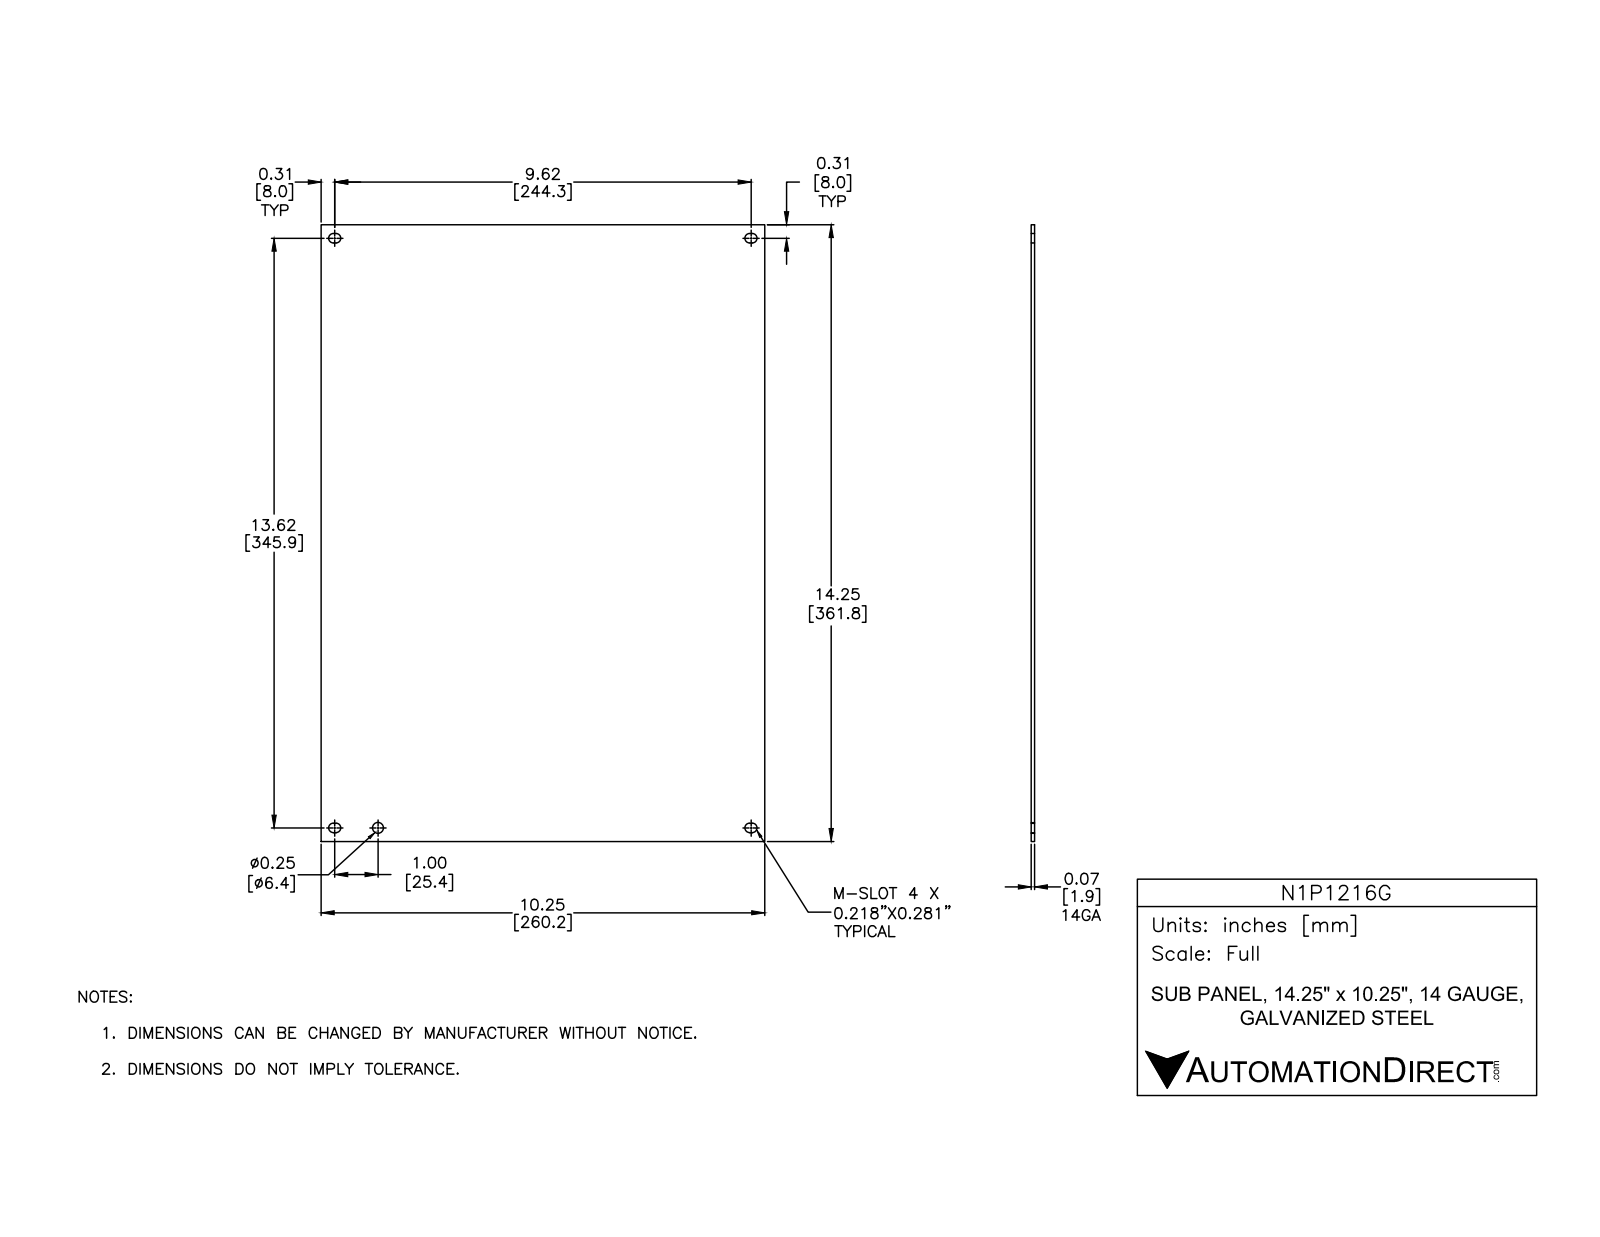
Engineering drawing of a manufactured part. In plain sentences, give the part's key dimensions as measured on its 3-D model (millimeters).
The part is named "N1P1216". Its 3-D file was written by "Autodesk Inventor 2012 (AUTOMOTIVE_DESIGN)". It is 1 solid with 23 faces: 14 planar, 9 cylindrical and 0 other. Overall it measures 362 by 260.4 by 1.9 millimeters. Its volume is 176 800 cubic millimeters and its surface area 190 600 square millimeters. Round holes: 1 of diameter 6.4. Partial cylindrical surfaces (rounded edges, fillets, slot ends): 8 of radius 3.2. The main face-to-face distances are 1.9, 260.4, 362, 11.1, 350.8, 4.8, 357.2, 6.4, 346, 339.7.
